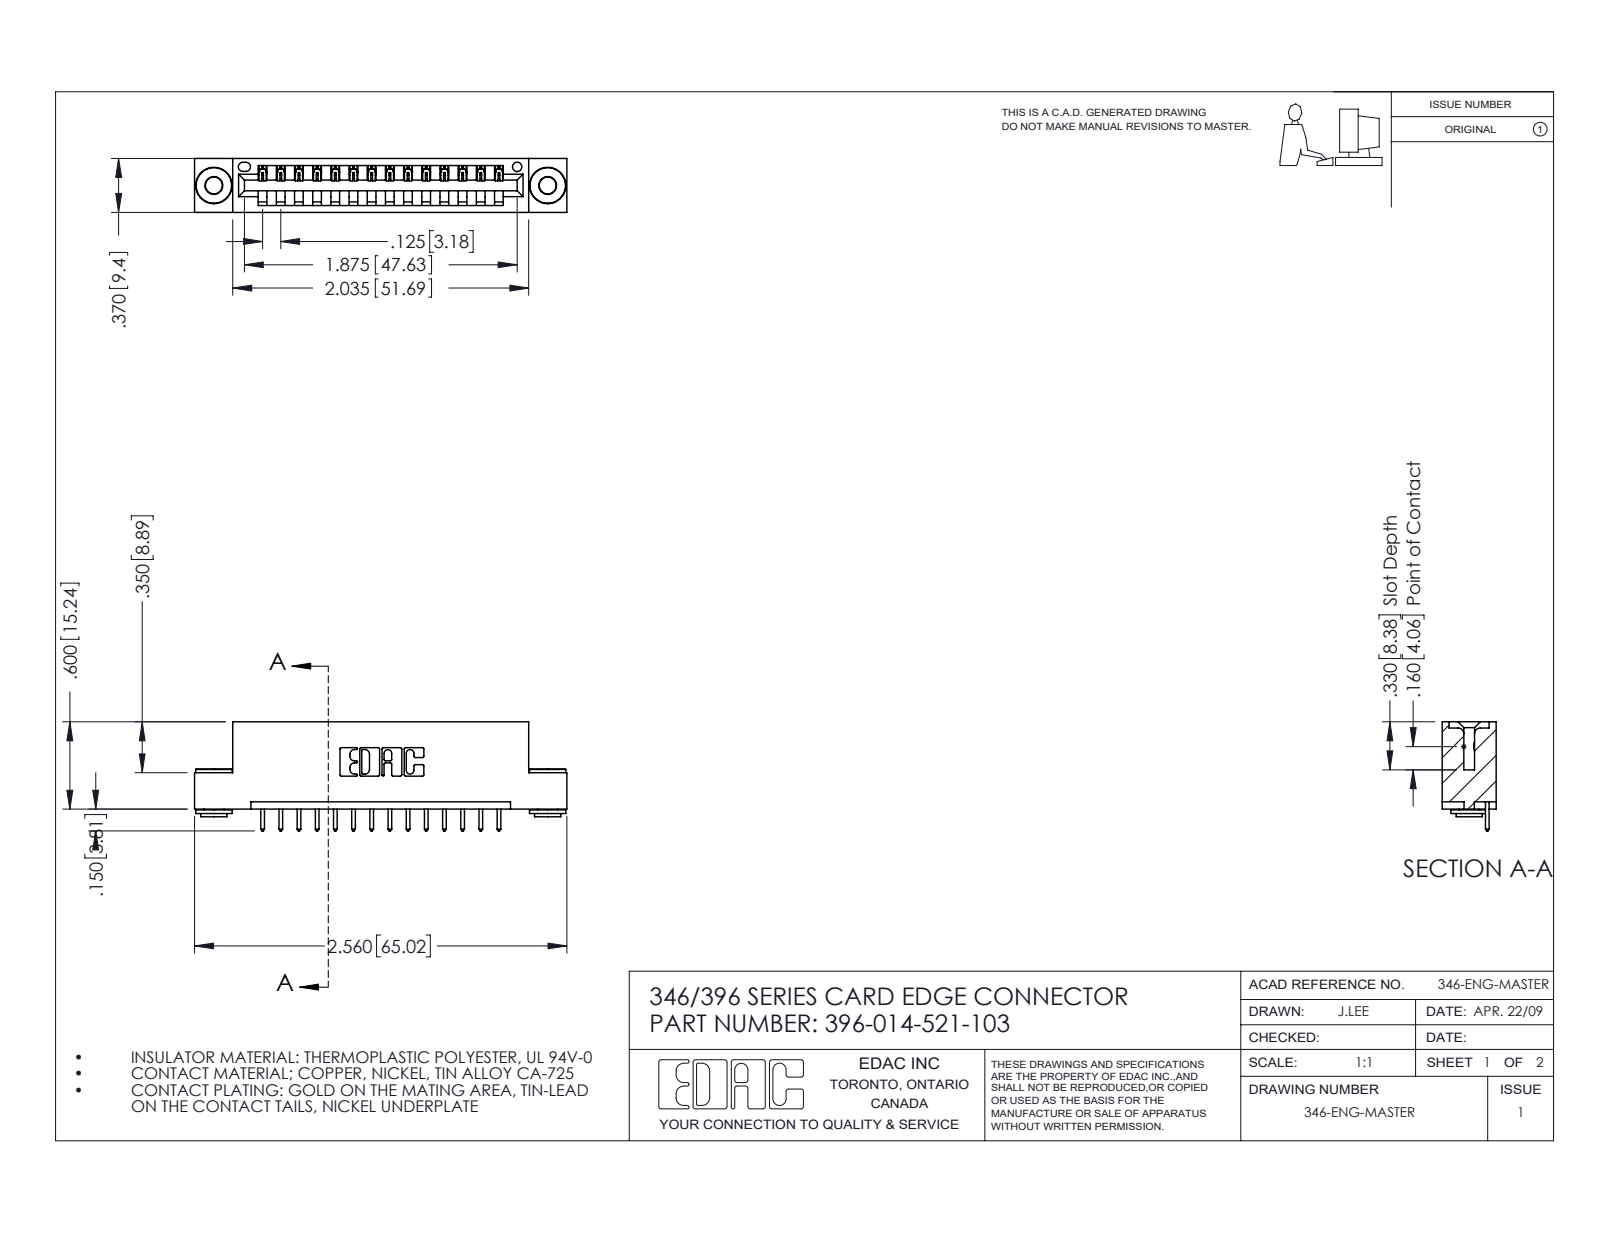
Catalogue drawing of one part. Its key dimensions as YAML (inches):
part_name: "396-014-521-103; 345-292-001_345-293-121; 346 Part_Flush Mounting Lugs - 0.156 Dia-TH; 345-250-002_345-250-002-102"
step_written_by: "SolidWorks 2016 (CONFIG_CONTROL_DESIGN)"
units: inches
bodies: {solids: 17, faces: 972, planar: 646, cylindrical: 318, other: 8}
overall_size: [2.56, 0.75, 0.37]
volume: 0.367
surface_area: 11.27
round_holes:
  - {diameter: 0.116, count: 2}
  - {diameter: 0.156, count: 2}
  - {diameter: 0.064, count: 1}
round_bosses_or_shafts:
  - {diameter: 0.25, count: 2}
  - {diameter: 0.18, count: 2}
  - {diameter: 0.136, count: 2}
partial_cylinders:
  - {radius: 0.006, count: 28}
  - {radius: 0.01, count: 28}
  - {radius: 0.01, count: 22}
  - {radius: 0.007, count: 6}
  - {radius: 0.031, count: 6}
  - {radius: 0.026, count: 3}
  - {radius: 0.031, count: 2}
  - {radius: 0.04, count: 2}
face_to_face_distances: [0.25, 0.048, 0.322, 0.37, 0.025, 0.072, 0.298, 0.148, 0.222, 0.1]
hole_center_spacings: [0.246, 2.089, 2.295]
